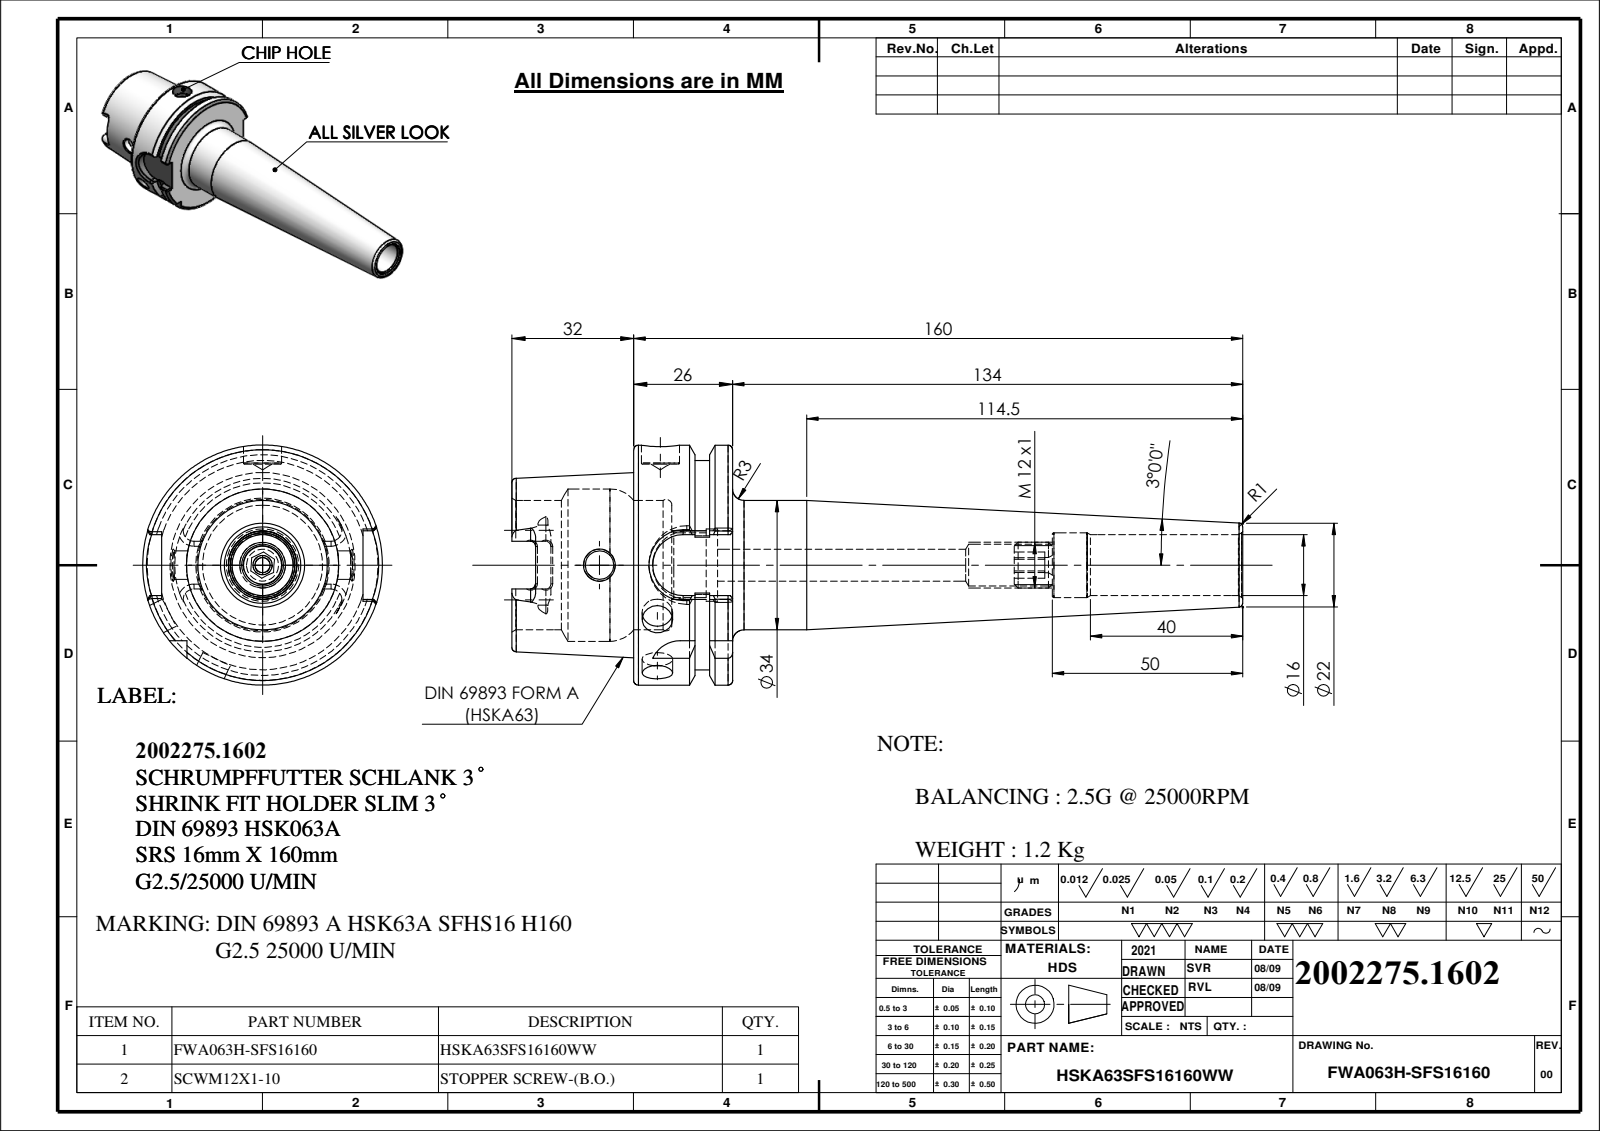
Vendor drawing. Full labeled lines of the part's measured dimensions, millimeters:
Part name (STEP PRODUCT): SCWM12X1-10; HSKA63SFC16160WW; 9163A-SRS16160
STEP written by: SolidWorks 2018 (CONFIG_CONTROL_DESIGN)
Units: millimetres
Bodies: 2 solids, 196 faces (59 planar, 57 cylindrical, 80 other)
Overall size (bounding box): 191.95 × 63 × 63
Volume: 155 261 mm³ · Surface area: 39 462 mm²
Round holes (diameter × count): ⌀8 ×2, ⌀4 ×1, ⌀7.5 ×1, ⌀8.4 ×1, ⌀10 ×1, ⌀11 ×1, ⌀16 ×1, ⌀17 ×1, ⌀19 ×1, ⌀34 ×1, ⌀40 ×1
Round bosses / shafts (diameter × count): ⌀63 ×1, ⌀55 ×1, ⌀12 ×1
Partial cylindrical surfaces — rounded edges, fillets, slot ends (radius × count): R1.3 ×6, R2.88 ×4, R8 ×2, R9 ×1
Main face-to-face distances: 25.95, 10, 15.95, 32, 42, 57.95, 52.9, 54, 22, 12
